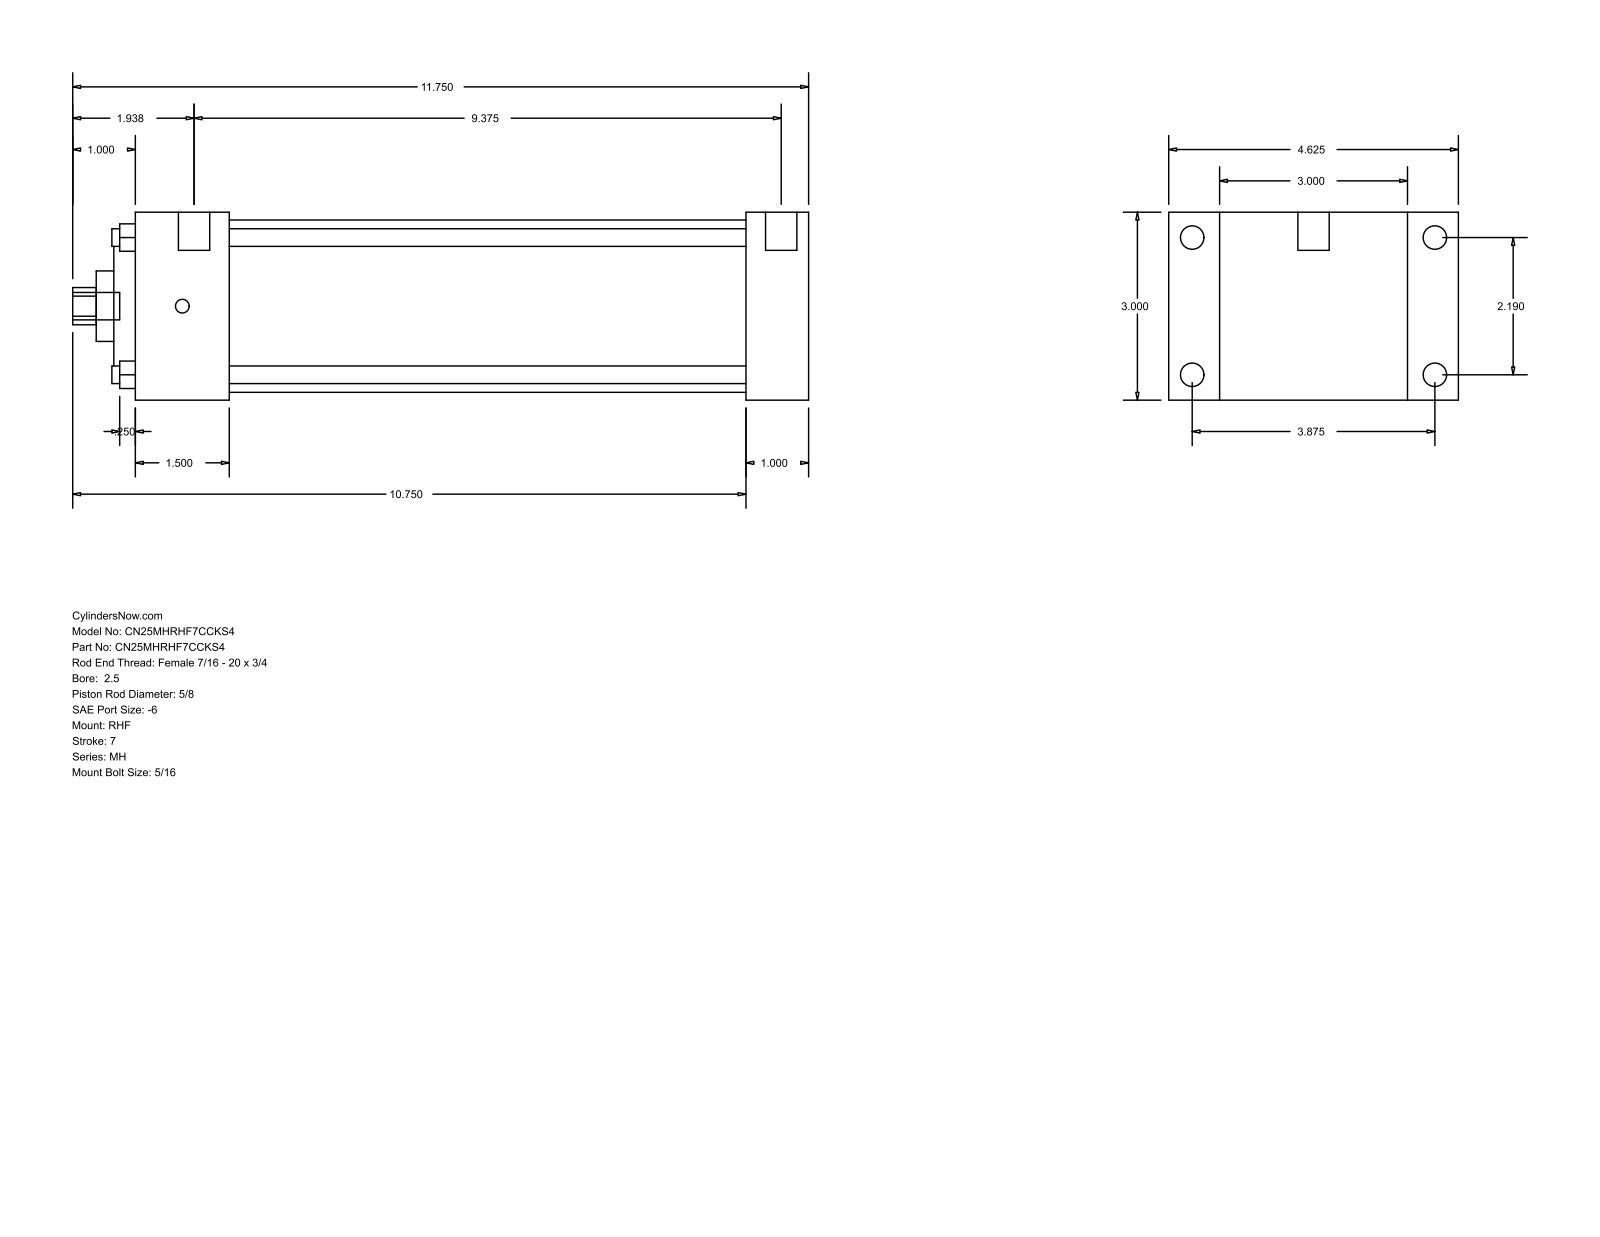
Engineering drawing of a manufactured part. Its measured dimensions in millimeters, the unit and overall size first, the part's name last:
Units: millimetres
Overall size (bounding box): 298.45 × 117.47 × 76.2
Round holes (diameter × count): ⌀7.14 ×4, ⌀15.88 ×1, ⌀28.57 ×1, ⌀55.55 ×1, ⌀69.85 ×1
Round bosses / shafts (diameter × count): ⌀9.53 ×4, ⌀5.56 ×4, ⌀12.7 ×2, ⌀11.11 ×1
Partial cylindrical surfaces — rounded edges, fillets, slot ends (radius × count): R7.54 ×1
Main face-to-face distances: 76.2, 25.4, 20.64, 96.84, 273.05, 247.65, 117.48, 38.1, 209.55, 234.95
Hole centre spacings: 39.33, 55.62, 78.66
Bodies: 0 solids, 90 faces (61 planar, 29 cylindrical, 0 other)
Part name (STEP PRODUCT): MH_RHF__0250_0.625
STEP written by: GSSL Pune (CONFIG_CONTROL_DESIGN)
